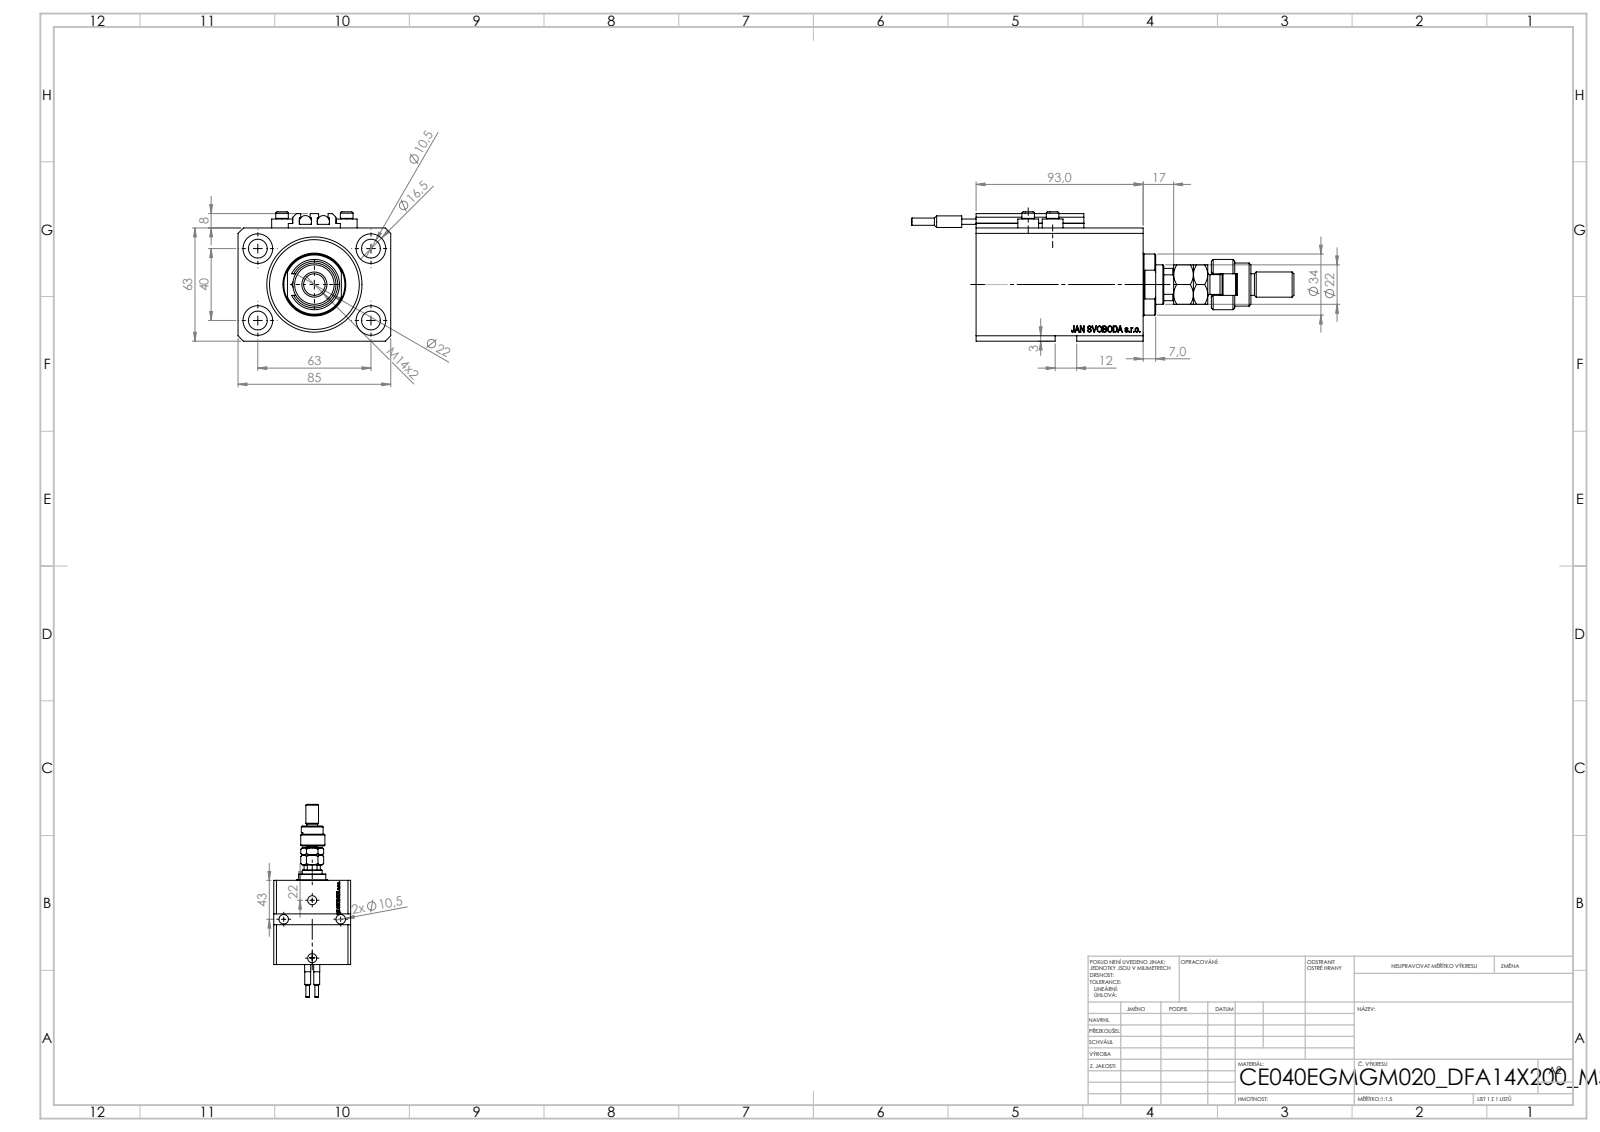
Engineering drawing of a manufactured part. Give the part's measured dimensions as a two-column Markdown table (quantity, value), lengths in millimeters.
| quantity | value |
| --- | --- |
| part name | ALLEN BOLT V250CE; SWITCH_V250CE; V250CE_E_Body; MFA (+3 more) |
| STEP written by | SolidWorks 2019 (CONFIG_CONTROL_DESIGN) |
| units | millimeters |
| bodies | 12 solids, 1224 faces (595 planar, 151 cylindrical, 478 other) |
| overall size | 213 × 85 × 72 |
| volume | 462 740 mm³ |
| surface area | 106 498 mm² |
| round holes (diameter × count) | 10.5 × 6, 1.25 × 4, 4 × 4, 16.5 × 4, 10 × 2, 13.16 × 2, 20 × 2, 12.5 × 1, 22 × 1, 40 × 1, 53 × 1 |
| round bosses / shafts (diameter × count) | 11.6 × 4, 7 × 4, 6.8 × 2, 6.5 × 2, 4 × 2, 34 × 1, 28 × 1, 24 × 1 |
| partial cylindrical surfaces (radius × count) | 0.2 × 10, 9.75 × 1, 10.5 × 1 |
| main face-to-face distances | 63, 85, 93, 17, 76, 3, 11.4, 64.6, 81.6, 65 |
| hole center spacings | 37.31, 63, 13.6, 15.4, 24.96, 28.02, 28.43, 33.62 |
